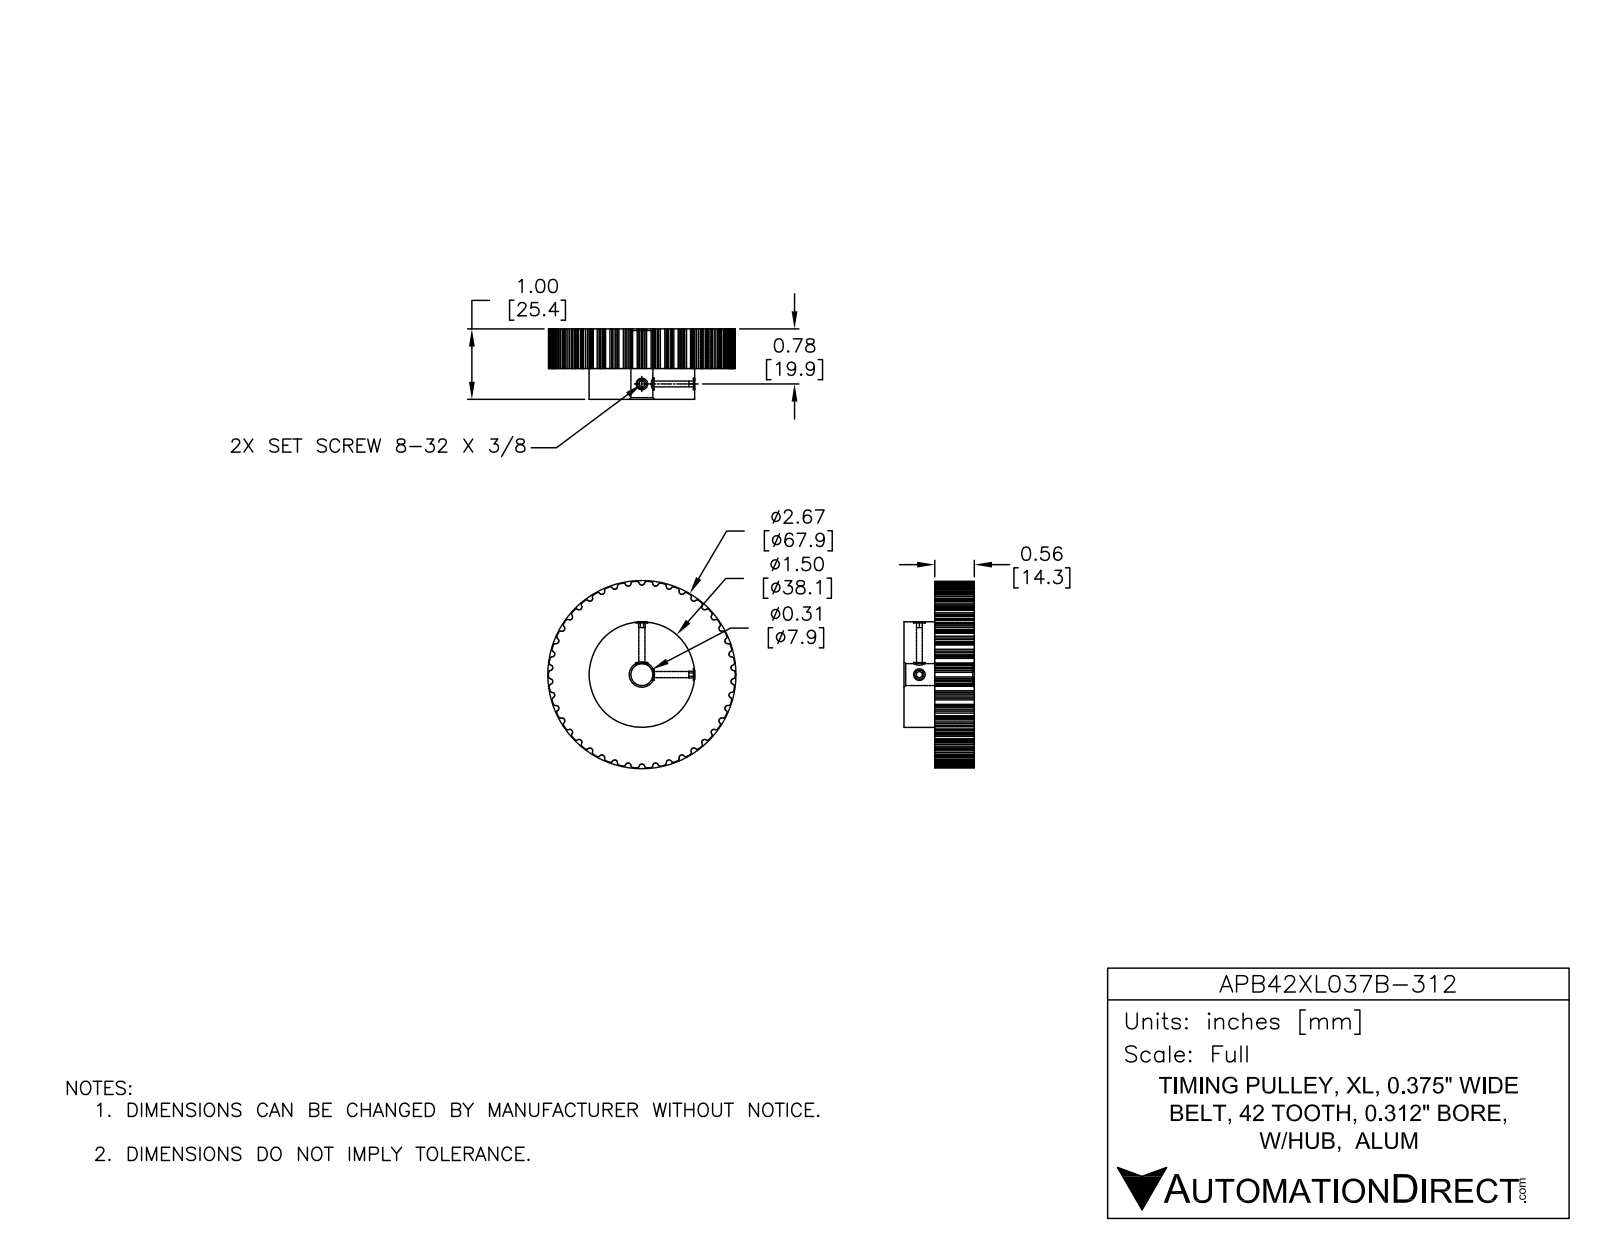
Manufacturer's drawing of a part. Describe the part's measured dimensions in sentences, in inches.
The part is named "APB42XL037B-312". Its 3-D file was written by "SolidWorks 2014 (AUTOMOTIVE_DESIGN)". It is 1 solid with 390 faces: 87 planar, 293 cylindrical and 10 other. Overall it measures 2.654 by 2.651 by 1 inches. Its volume is 3.692 cubic inches and its surface area 19.92 square inches. Round holes: 2 of diameter 0.088, 1 of diameter 0.313. Round bosses or shafts: 1 of diameter 1.5. Partial cylindrical surfaces (rounded edges, fillets, slot ends): 168 of radius 0.015, 1 of radius 1.272, 1 of radius 1.327. The main face-to-face distances are 0.56, 1, 0.44, 1.028, 1.029, 1.03, 1.031.
